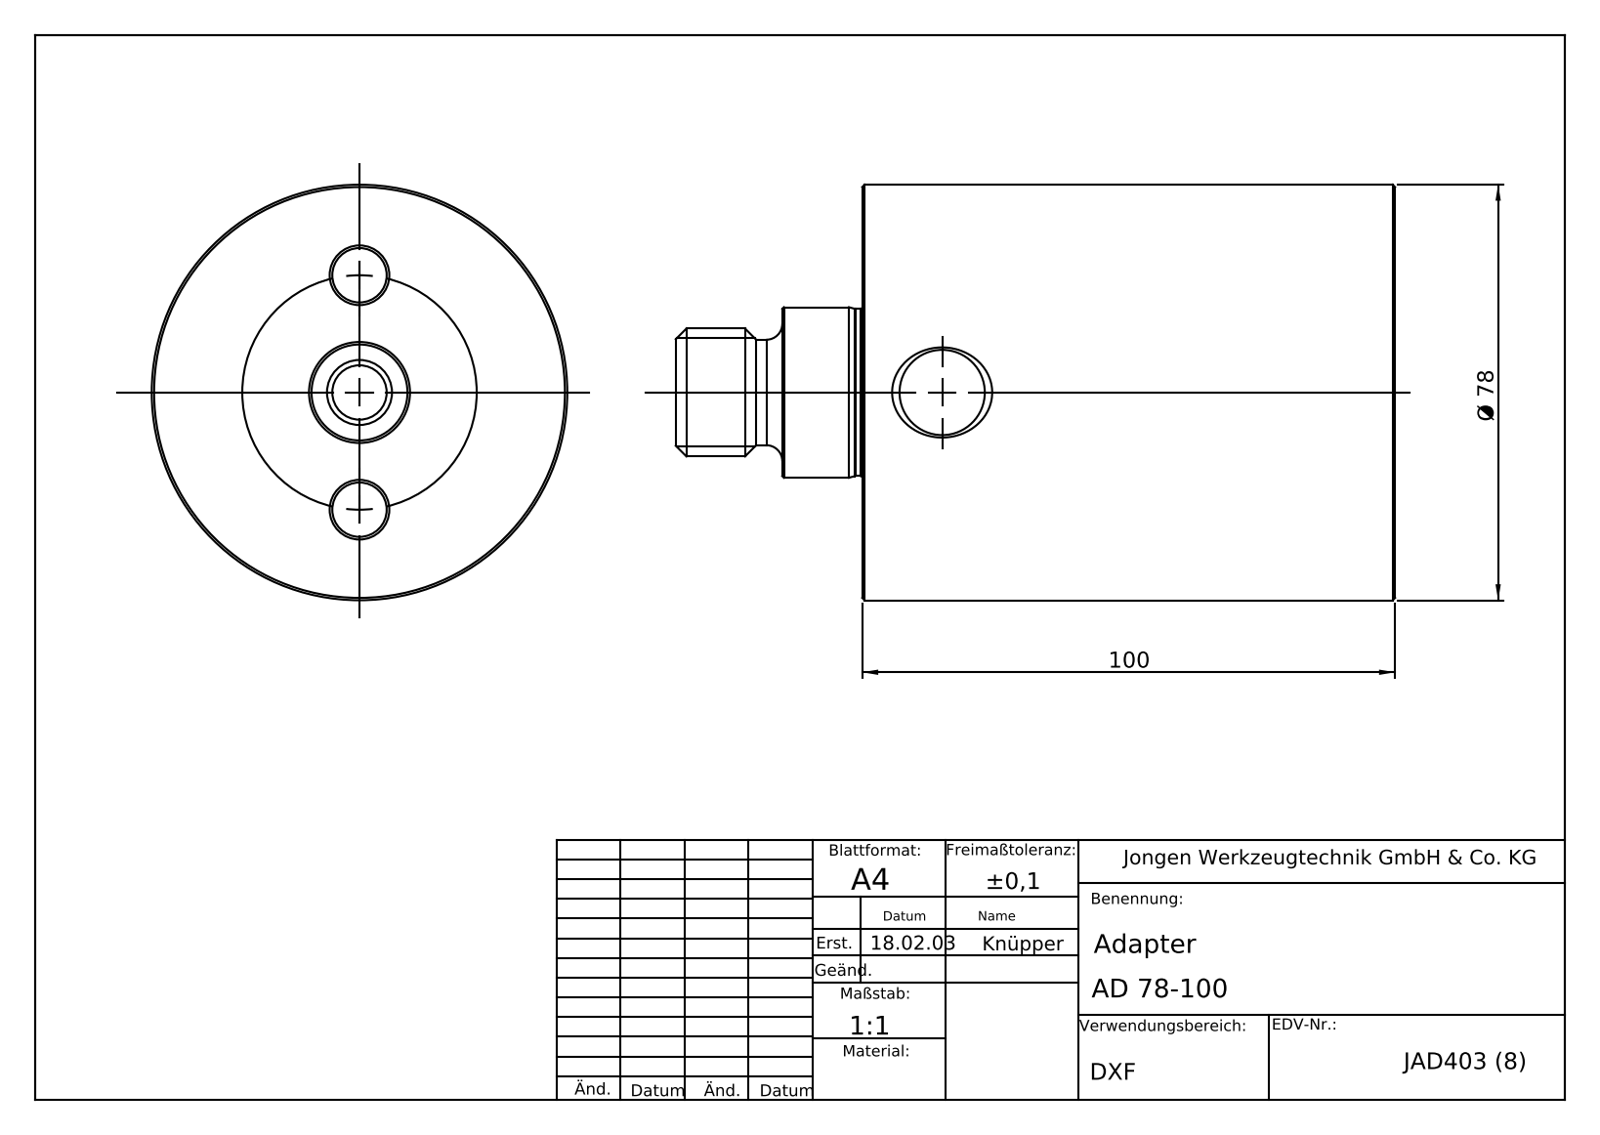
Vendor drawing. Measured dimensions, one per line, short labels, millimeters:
name: AD 78-100
written by: SolidWorks 2014 (AUTOMOTIVE_DESIGN)
unit: mm
bodies: 1 solid, 38 faces (5 planar, 12 cylindrical, 21 other)
size: 135 × 78 × 78
volume: 481 072 mm³; area: 41 415 mm²
holes: 2× ⌀10.2, 1× ⌀3.15, 1× ⌀16, 1× ⌀18, 1× ⌀18.2
bosses: 1× ⌀78, 1× ⌀32, 1× ⌀31.4, 1× ⌀24, 1× ⌀19.8
face distances: 100, 35, 135, 20, 15, 115, 127, 107, 92, 8
hole spacings: 22
